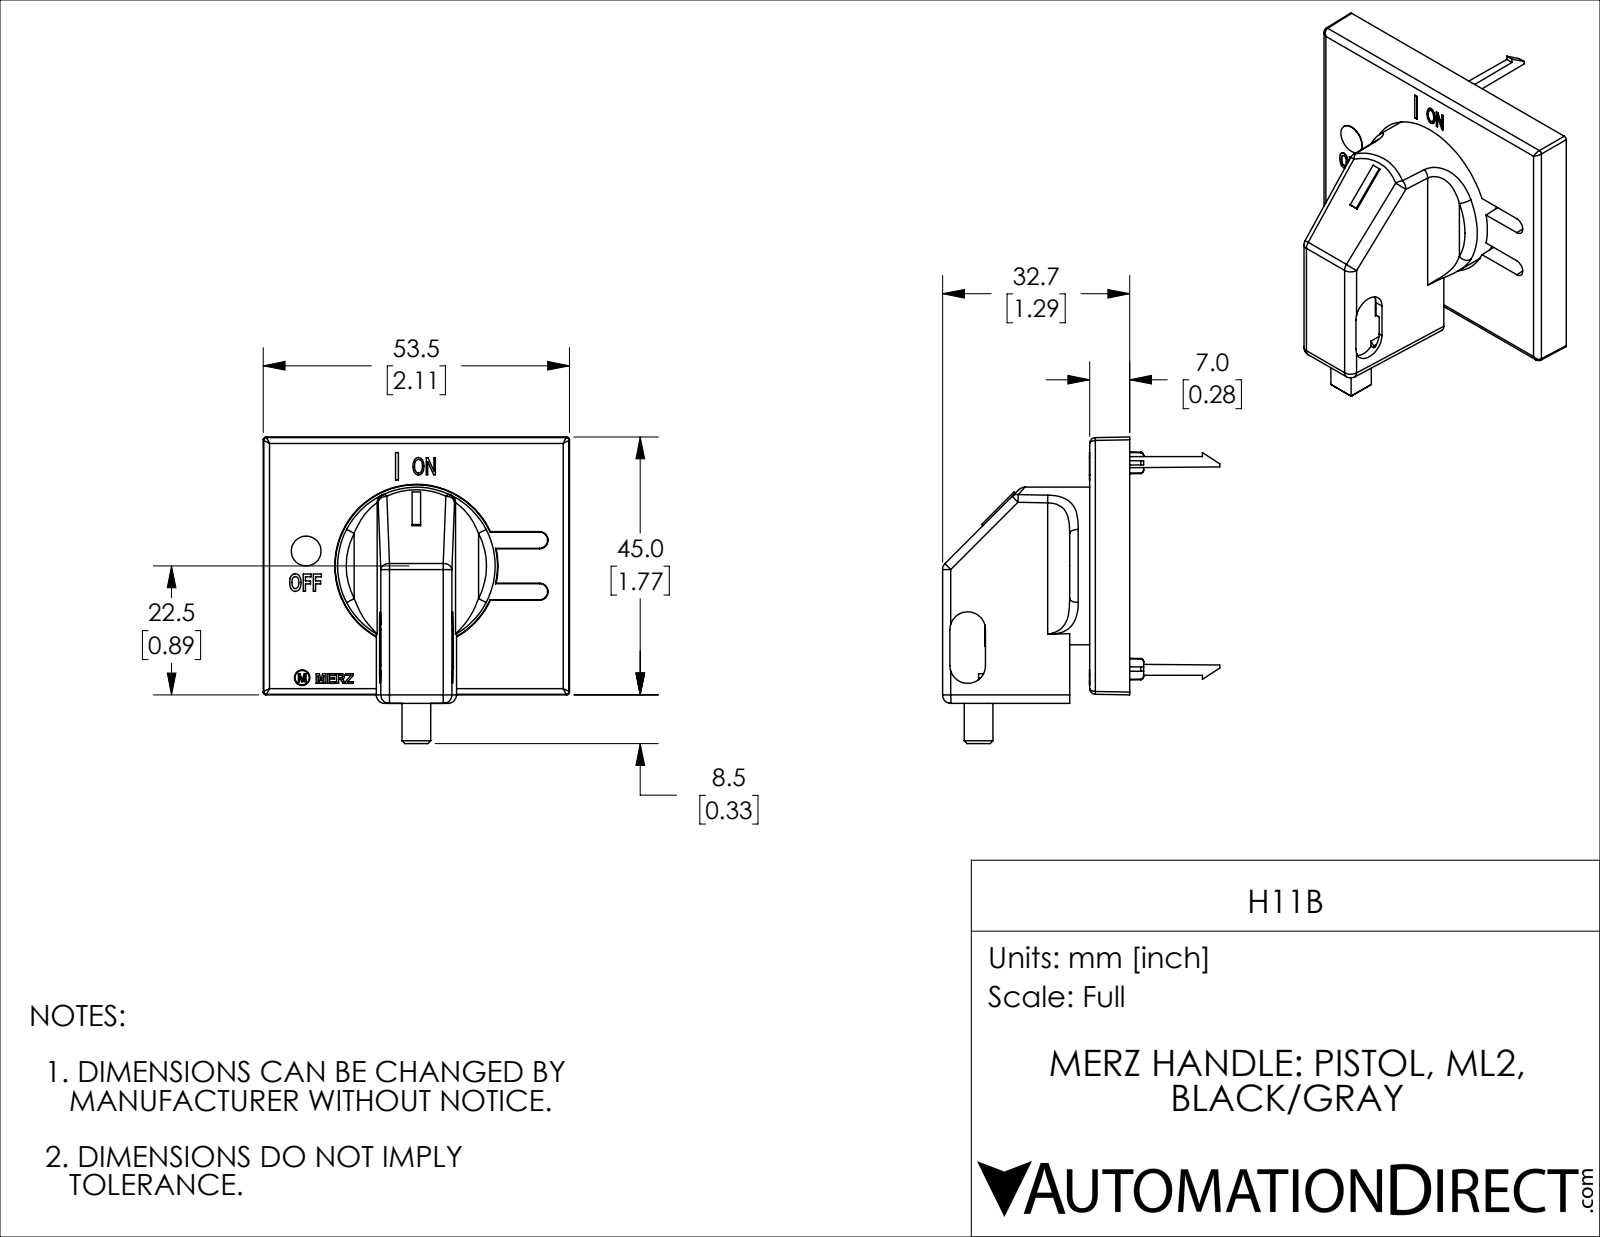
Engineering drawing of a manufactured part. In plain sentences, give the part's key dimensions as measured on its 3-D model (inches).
The part is named "H11B". Its 3-D file was written by "SolidWorks 2019 (AUTOMOTIVE_DESIGN)". It is 2 solids with 439 faces: 290 planar, 42 cylindrical and 107 other. Overall it measures 2.106 by 2.106 by 1.907 inches. Its volume is 1.019 cubic inches and its surface area 24.13 square inches. Round holes: 1 of diameter 0.098. Round bosses or shafts: 1 of diameter 1.083, 1 of diameter 0.205, 1 of diameter 0.106. Partial cylindrical surfaces (rounded edges, fillets, slot ends): 8 of radius 0.059, 6 of radius 0.02, 5 of radius 0.012, 4 of radius 0.039, 2 of radius 0.122, 2 of radius 0.157. The main face-to-face distances are 0.039, 0.079, 0.157, 0.197, 0.118, 0.236, 0.276, 0.325, 0.033, 0.094.
